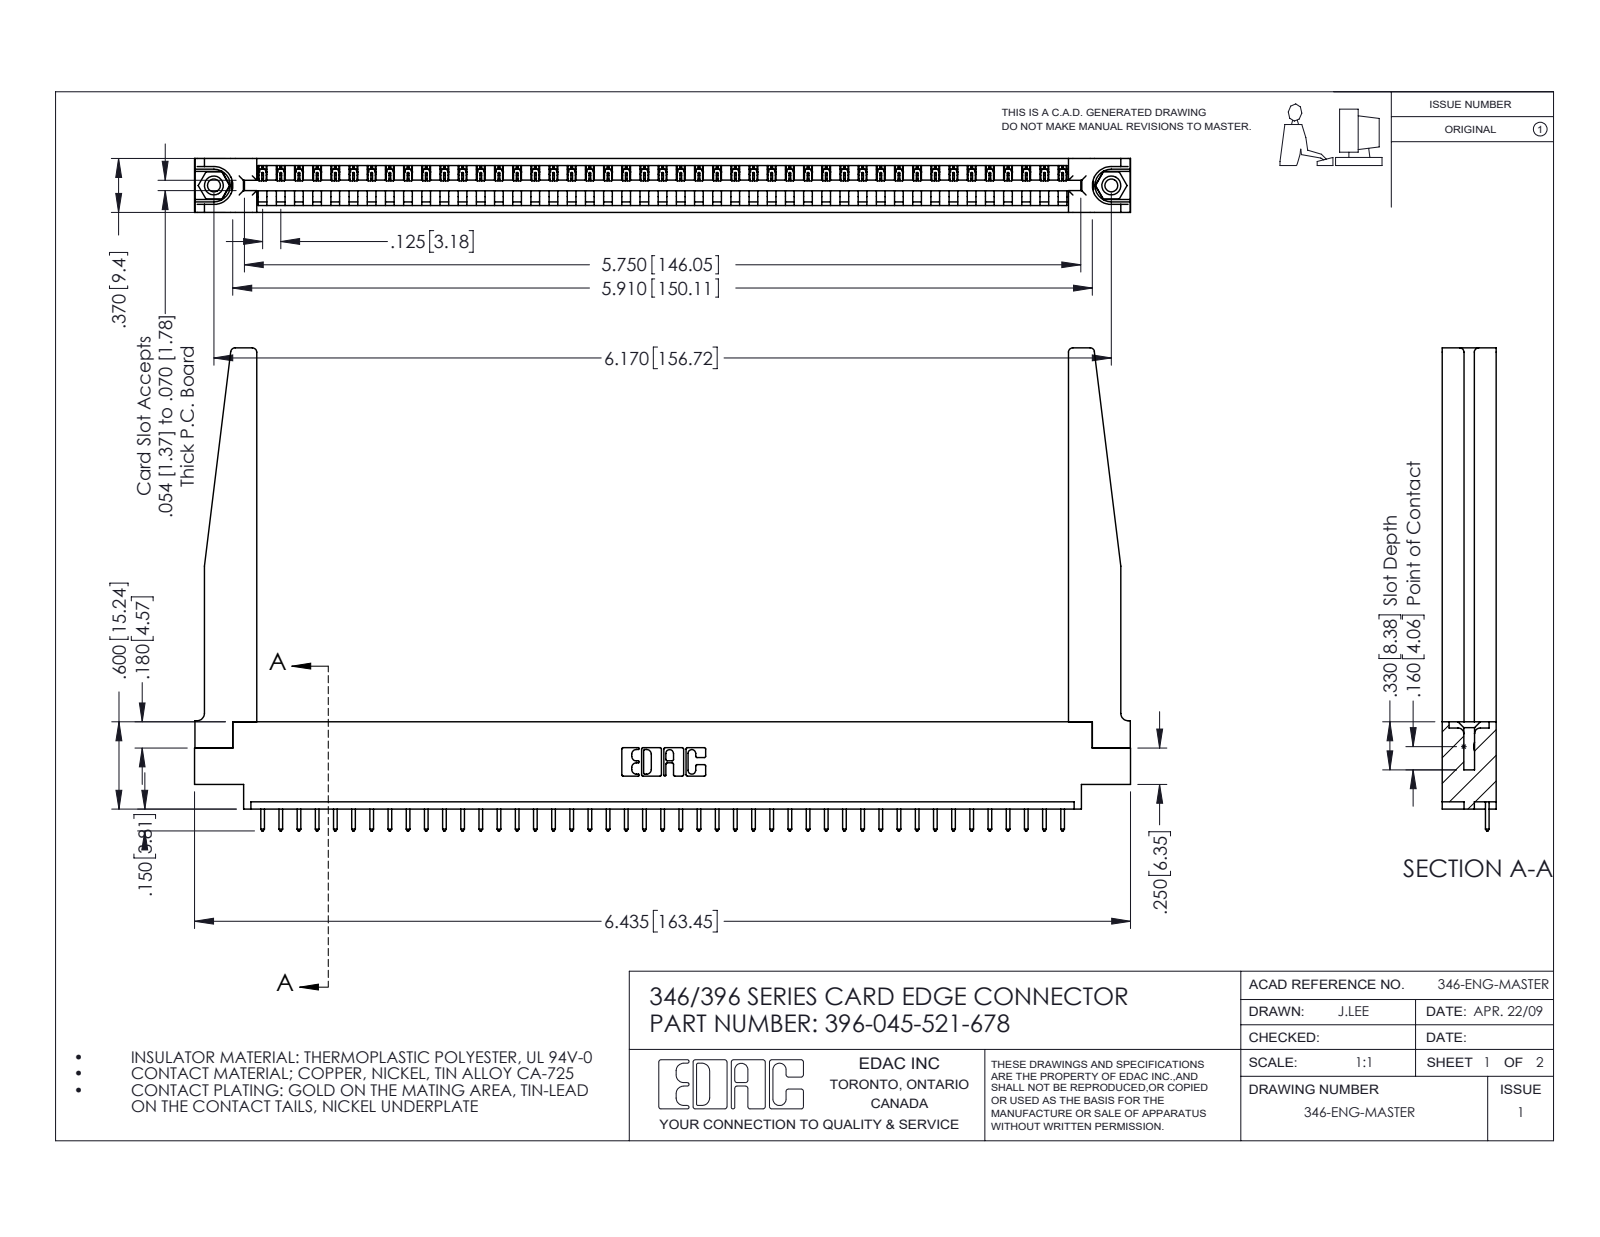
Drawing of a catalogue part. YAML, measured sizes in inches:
part_name: "345-250-001_345-250-001-102; 396-045-521-678; 346 Part_0.170 Offset - 0.156 Dia-TH; 346-220-078_345-220-078 (+1 more)"
step_written_by: "SolidWorks 2016 (CONFIG_CONTROL_DESIGN)"
units: inches
bodies: {solids: 50, faces: 2970, planar: 2022, cylindrical: 896, other: 52}
overall_size: [6.435, 3.32, 0.37]
volume: 1.36
surface_area: 39.45
round_holes:
  - {diameter: 0.089, count: 2}
  - {diameter: 0.125, count: 2}
  - {diameter: 0.156, count: 2}
  - {diameter: 0.064, count: 1}
round_bosses_or_shafts:
  - {diameter: 0.155, count: 2}
partial_cylinders:
  - {radius: 0.006, count: 90}
  - {radius: 0.01, count: 90}
  - {radius: 0.01, count: 22}
  - {radius: 0.03, count: 8}
  - {radius: 0.007, count: 6}
  - {radius: 0.031, count: 6}
  - {radius: 0.026, count: 3}
  - {radius: 0.031, count: 2}
face_to_face_distances: [0.37, 0.048, 0.322, 0.072, 0.148, 0.15, 0.25, 0.298, 0.025, 0.222]
hole_center_spacings: [0.246, 5.961, 6.17]
